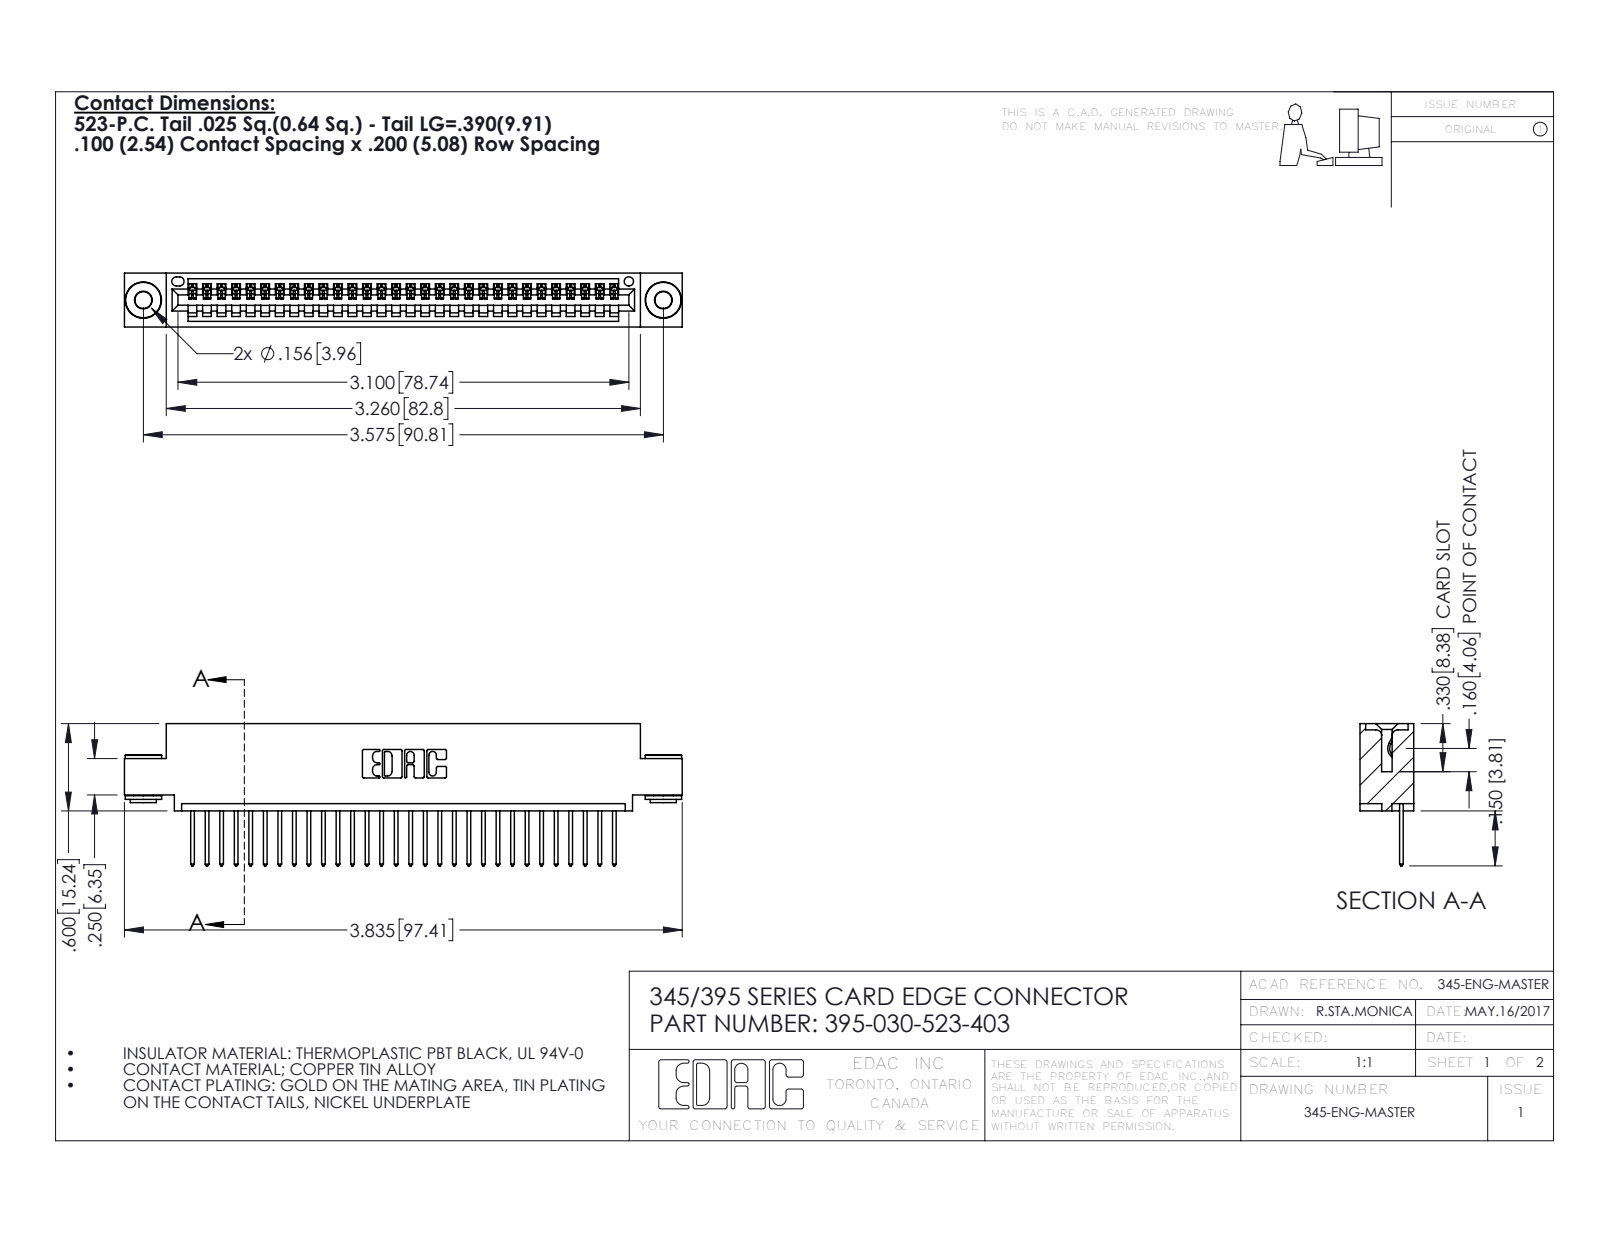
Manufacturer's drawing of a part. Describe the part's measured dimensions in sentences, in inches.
The part is named "345 Part_0.110 Offset - 0.156 Dia-TH; 395-030-523-403; 345-292-001_345-293-123; 345-250-002_345-250-002-102". Its 3-D file was written by "SolidWorks 2016 (CONFIG_CONTROL_DESIGN)". It is 33 solids with 1908 faces: 1294 planar, 606 cylindrical and 8 other. Overall it measures 3.835 by 0.977 by 0.37 inches. Its volume is 0.555 cubic inches and its surface area 18.98 square inches. Round holes: 2 of diameter 0.116, 2 of diameter 0.156, 1 of diameter 0.064. Round bosses or shafts: 2 of diameter 0.25, 2 of diameter 0.18, 2 of diameter 0.136. Partial cylindrical surfaces (rounded edges, fillets, slot ends): 60 of radius 0.006, 60 of radius 0.01, 22 of radius 0.01, 6 of radius 0.007, 6 of radius 0.031, 3 of radius 0.026, 2 of radius 0.031, 2 of radius 0.04. The main face-to-face distances are 0.072, 0.298, 0.37, 0.2, 0.025, 0.098, 0.272, 0.225, 0.149, 0.072. The hole center spacings are 0.27, 3.34, 3.575.
